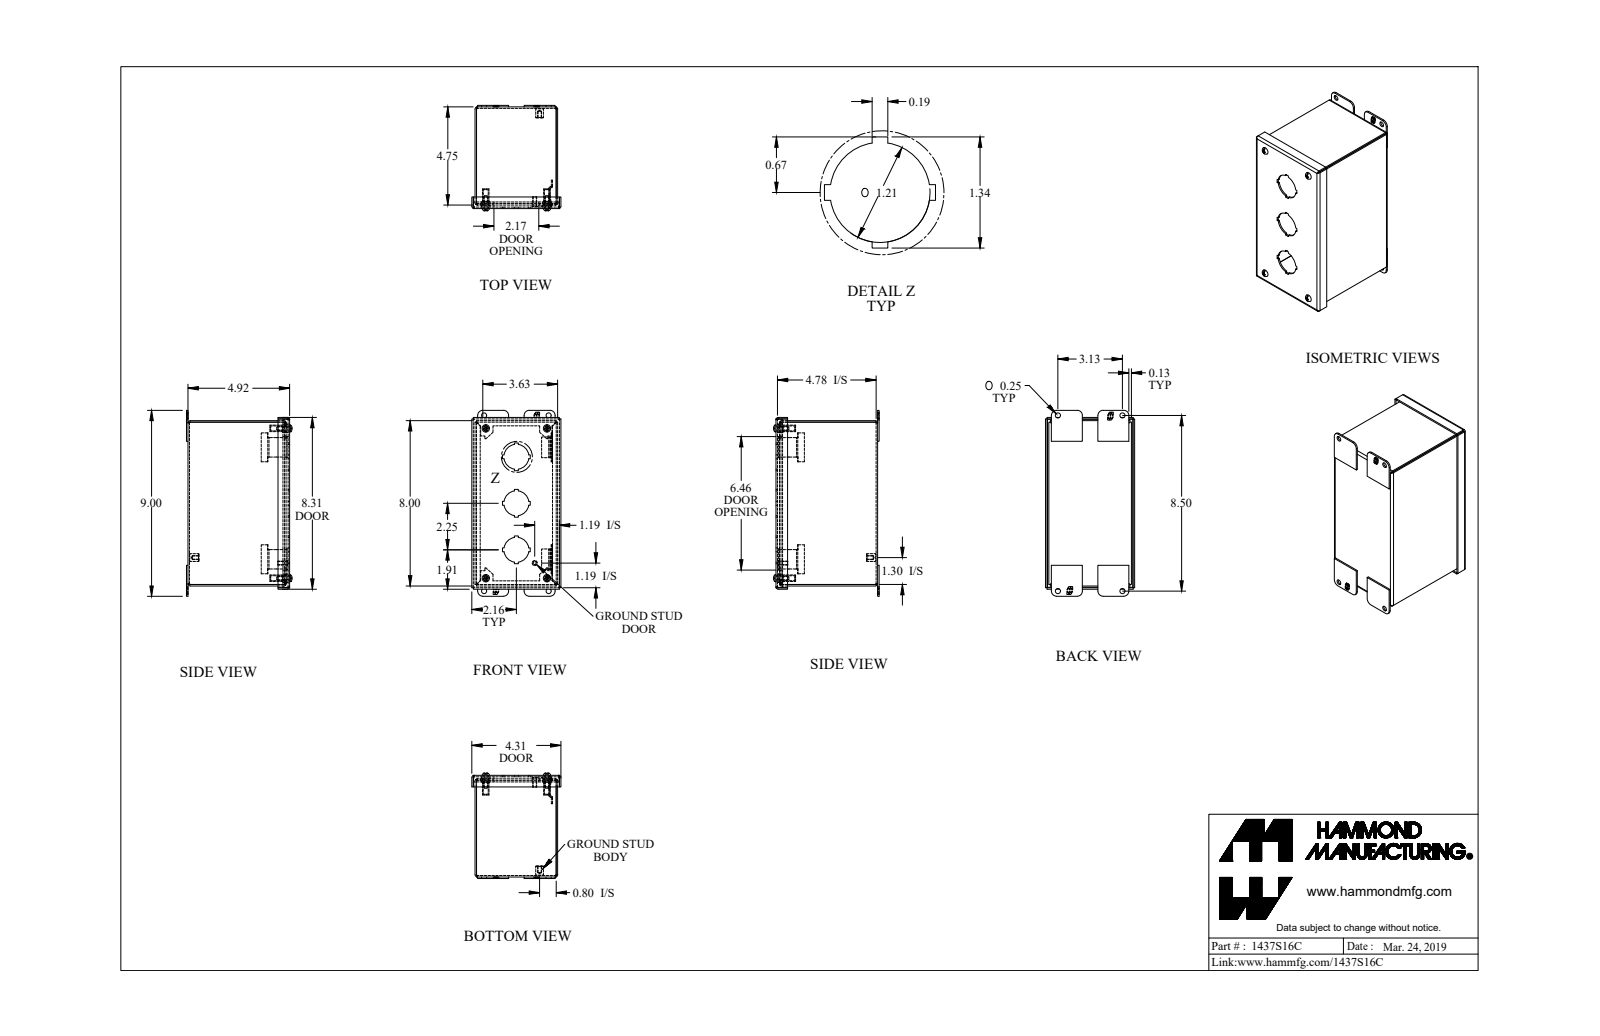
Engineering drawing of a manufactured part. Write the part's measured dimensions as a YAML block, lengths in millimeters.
part_name: "1437S16C_Default"
step_written_by: "SolidWorks 2019 (CONFIG_CONTROL_DESIGN)"
units: millimeters
bodies: {solids: 23, faces: 653, planar: 459, cylindrical: 164, other: 30}
overall_size: [228.6, 129.6, 109.5]
volume: 278300
surface_area: 293400
round_holes:
  - {diameter: 6.4, count: 8}
  - {diameter: 1.7, count: 4}
  - {diameter: 6.1, count: 4}
  - {diameter: 6.4, count: 4}
  - {diameter: 10.3, count: 4}
  - {diameter: 30.7, count: 3}
  - {diameter: 4, count: 1}
round_bosses_or_shafts:
  - {diameter: 4.8, count: 5}
  - {diameter: 10.3, count: 4}
  - {diameter: 8, count: 4}
  - {diameter: 3.8, count: 4}
  - {diameter: 9.5, count: 1}
  - {diameter: 6.4, count: 1}
partial_cylinders:
  - {radius: 0.9, count: 12}
  - {radius: 2.7, count: 12}
  - {radius: 6.4, count: 8}
  - {radius: 0.7, count: 4}
  - {radius: 2.2, count: 4}
  - {radius: 3.2, count: 4}
  - {radius: 4.3, count: 4}
face_to_face_distances: [1.8, 99.8, 123.2, 125, 101.6, 97.9, 201.4, 121.4, 4, 203.2]
hole_center_spacings: [184.2, 200.1, 16, 75.2, 78.9, 99.5, 153.9, 198.9]
